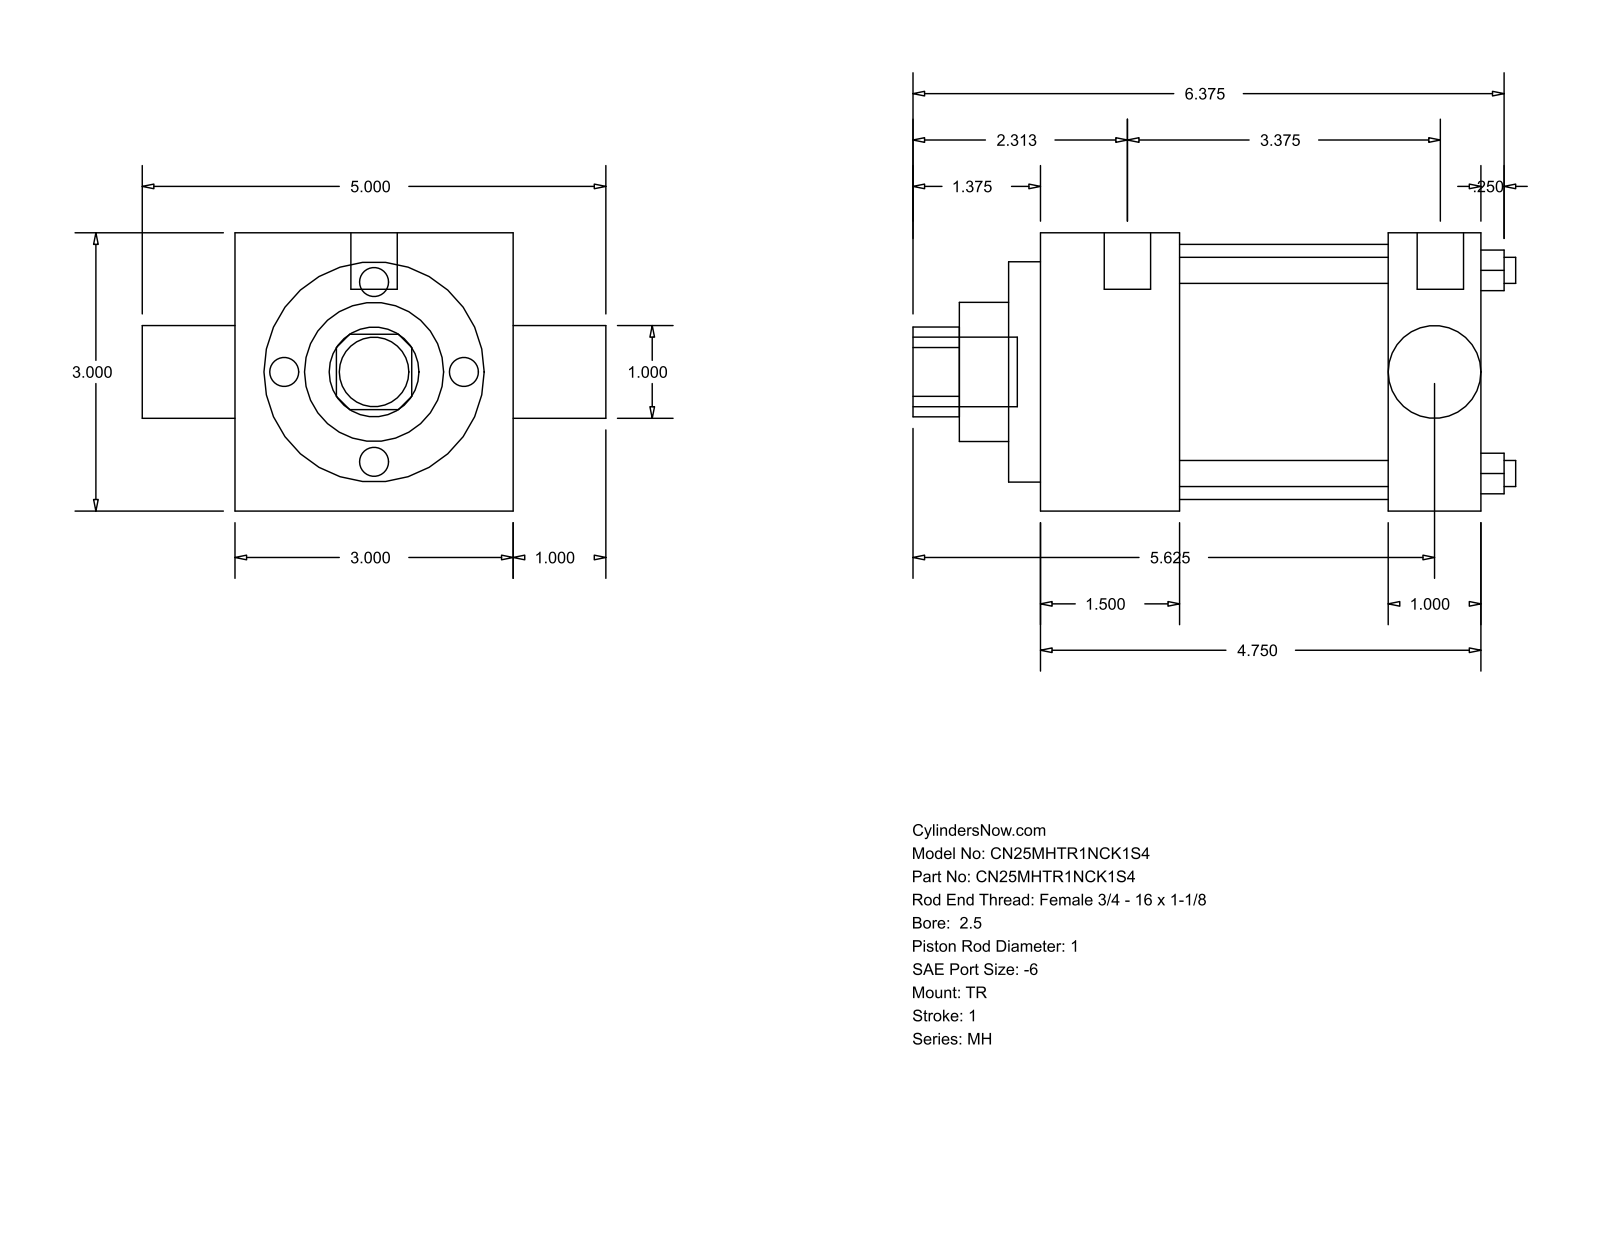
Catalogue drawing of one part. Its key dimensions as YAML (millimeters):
part_name: "MH_TR__0250_1"
step_written_by: "GSSL Pune (CONFIG_CONTROL_DESIGN)"
units: millimeters
bodies: {solids: 0, faces: 86, planar: 61, cylindrical: 25, other: 0}
overall_size: [165.1, 127, 76.2]
round_holes:
  - {diameter: 7.14, count: 4}
  - {diameter: 25.35, count: 1}
  - {diameter: 25.4, count: 1}
  - {diameter: 38.1, count: 1}
  - {diameter: 60.33, count: 1}
  - {diameter: 69.85, count: 1}
round_bosses_or_shafts:
  - {diameter: 5.56, count: 3}
  - {diameter: 12.7, count: 2}
  - {diameter: 19.05, count: 1}
partial_cylinders:
  - {radius: 12.29, count: 1}
face_to_face_distances: [76.2, 120.65, 25.39, 38.11, 82.54, 95.26, 57.15, 8.73, 46.84, 103.99]
hole_center_spacings: [39.33, 55.62, 78.66]
